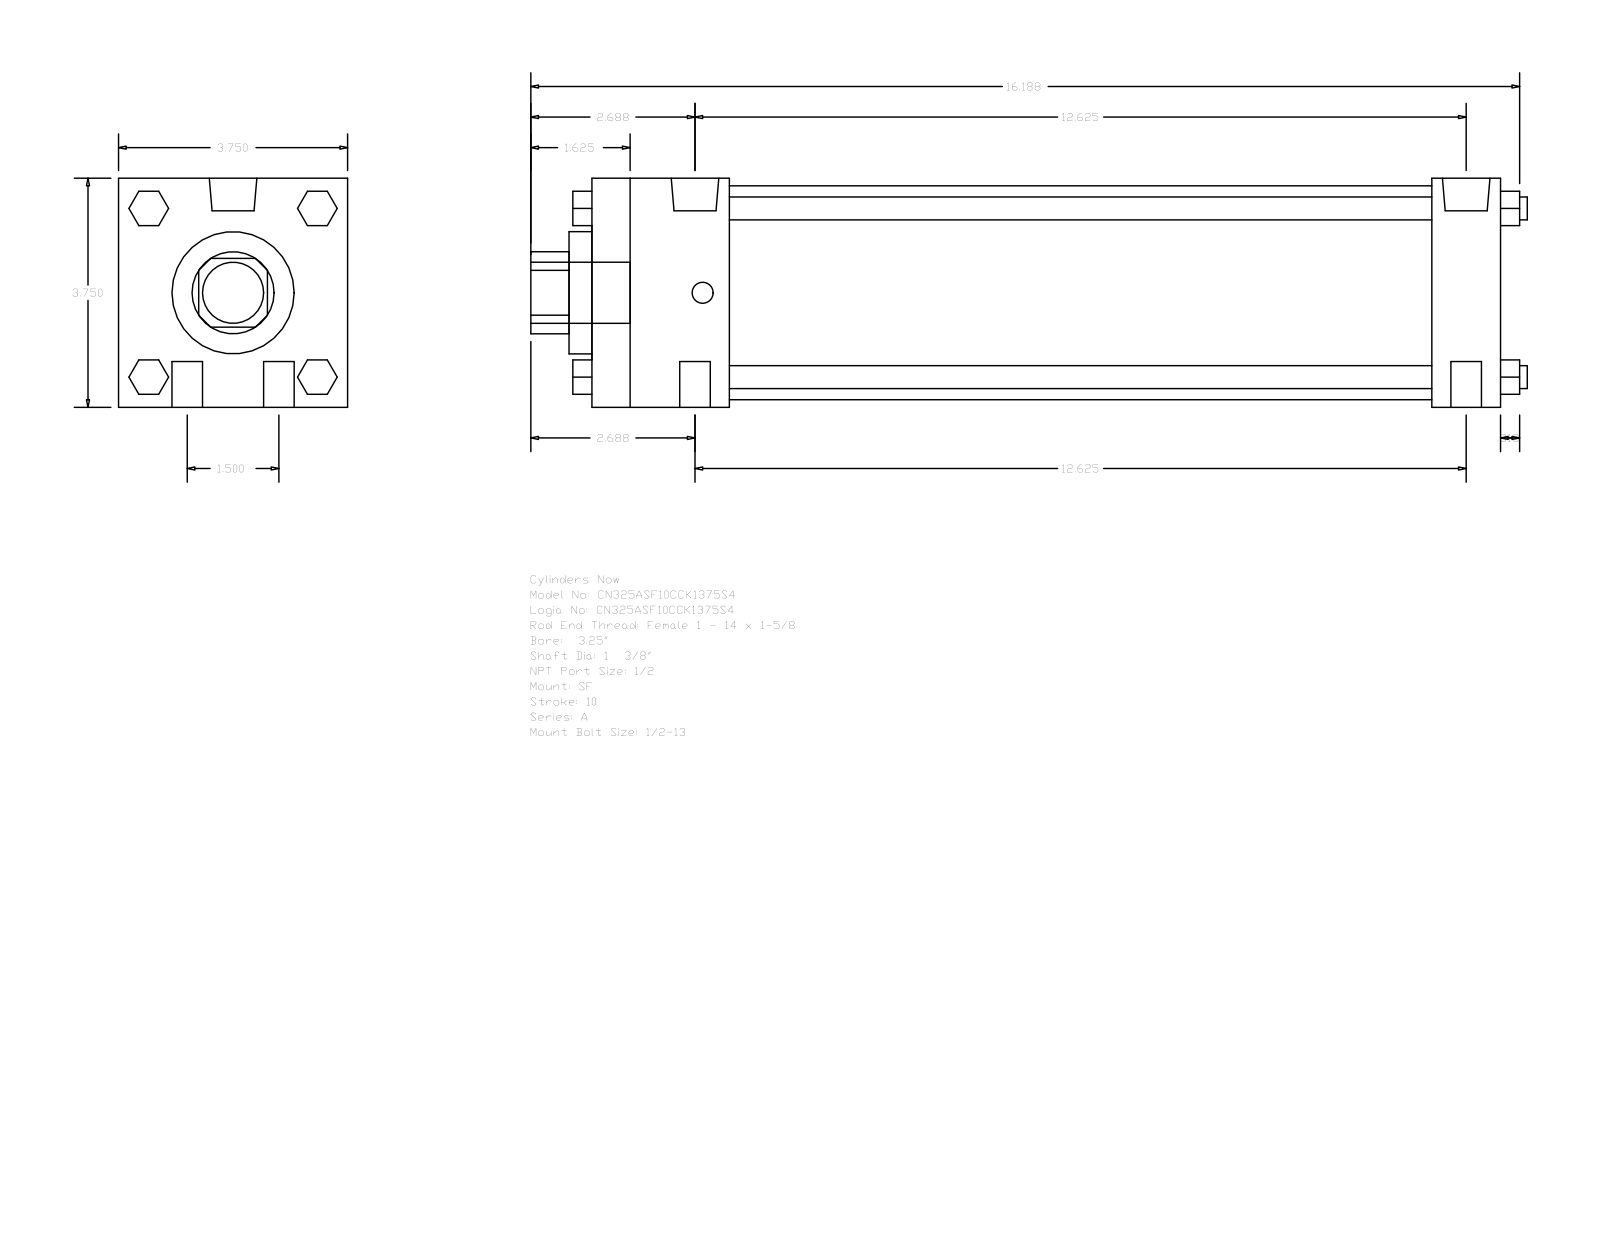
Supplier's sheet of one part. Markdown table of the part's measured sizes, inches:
| quantity | value |
| --- | --- |
| part name | A_SF__0325_1.375 |
| STEP written by | GSSL Pune (CONFIG_CONTROL_DESIGN) |
| units | inches |
| bodies | 0 solids, 124 faces (94 planar, 30 cylindrical, 0 other) |
| overall size | 16.313 × 3.75 × 3.75 |
| round holes (diameter × count) | 1.375 × 1, 2 × 1, 3.5 × 1 |
| round bosses / shafts (diameter × count) | 0.5 × 4, 0.375 × 4, 0.778 × 2, 0.344 × 2, 1 × 1 |
| partial cylindrical surfaces (radius × count) | 0.672 × 1 |
| main face-to-face distances | 3.75, 14.875, 1.125, 13.75, 2.25, 11.5, 12.625, 0.375, 2.625, 14.125 |
